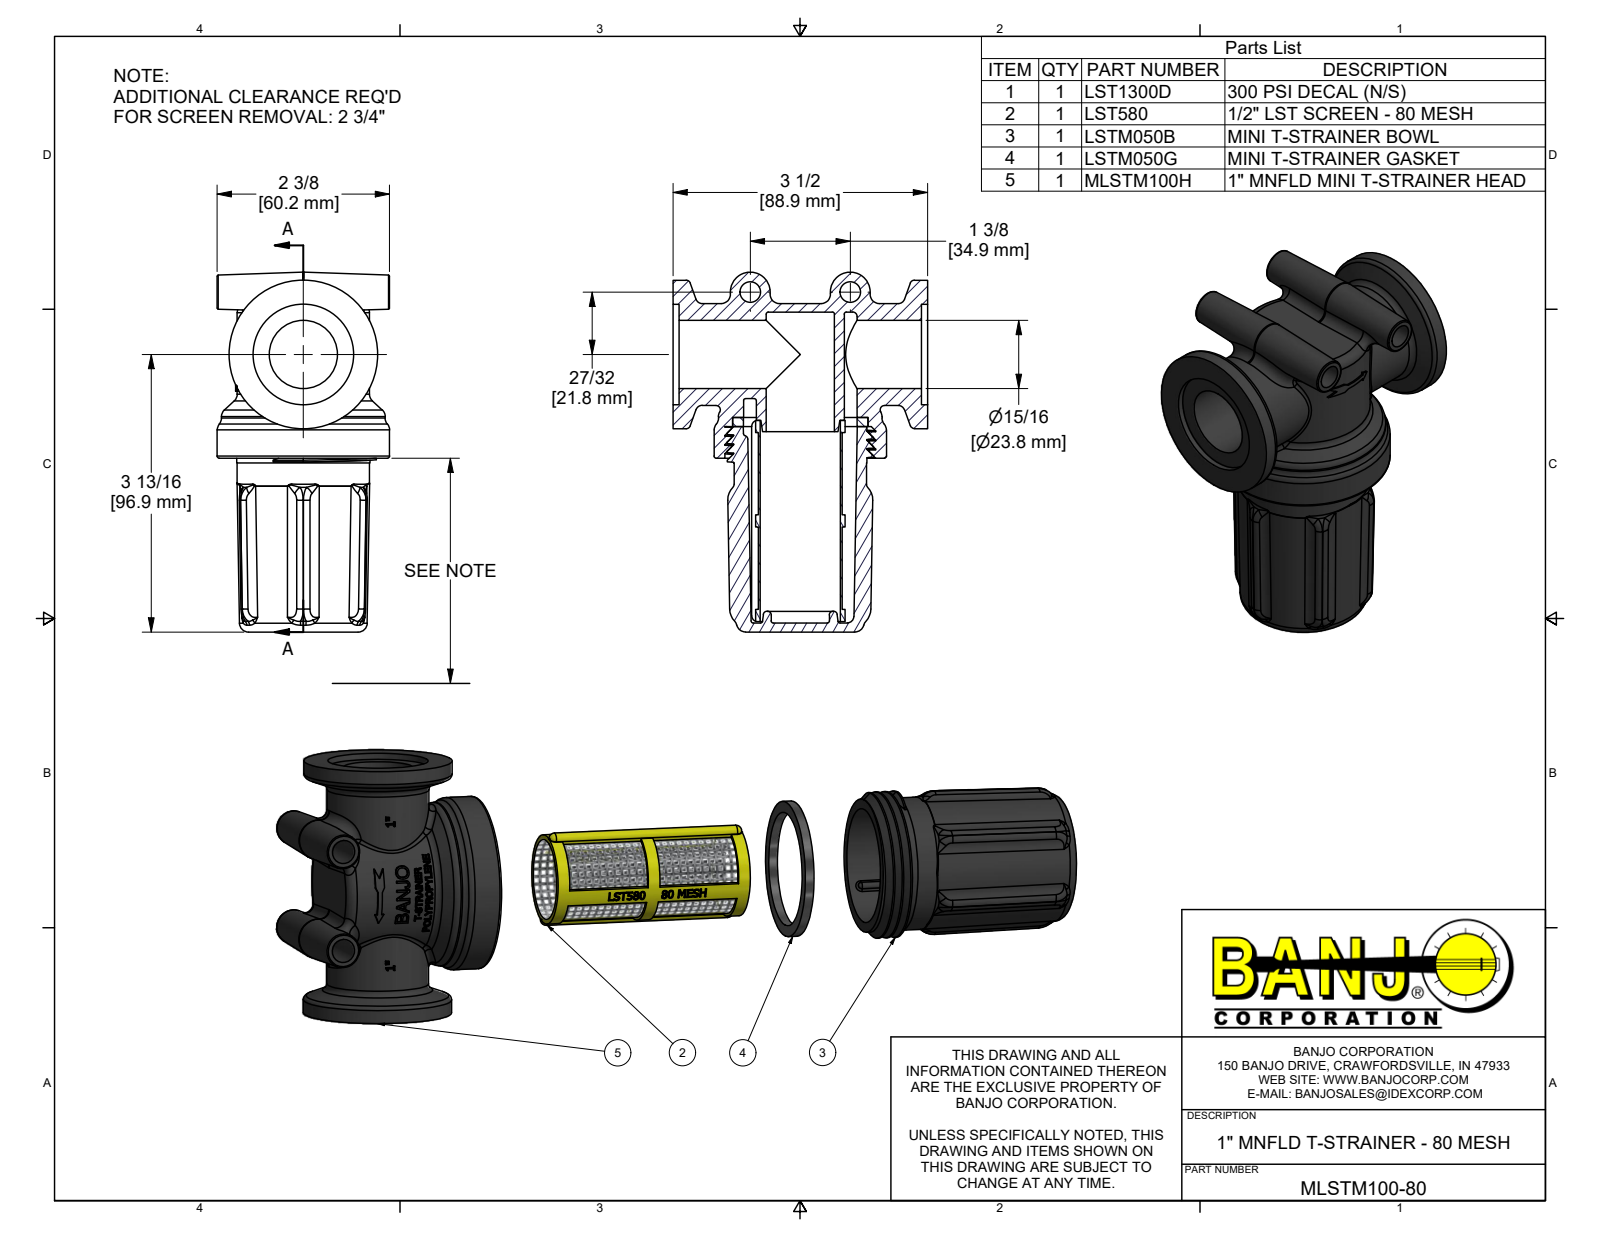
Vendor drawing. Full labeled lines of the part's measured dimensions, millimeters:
Part name (STEP PRODUCT): MLSTM100-80; MLSTM100H; LSTM050G; LSTM050B (+1 more)
STEP written by: Autodesk Inventor 2019 (AUTOMOTIVE_DESIGN)
Units: millimetres
Bodies: 4 solids, 1191 faces (524 planar, 152 cylindrical, 515 other)
Overall size (bounding box): 125.7 × 88.9 × 60.2
Volume: 148 700 mm³ · Surface area: 85 870 mm²
Round holes (diameter × count): ⌀23.8 ×2, ⌀20.3 ×1, ⌀28 ×1, ⌀35.1 ×1, ⌀39.6 ×1, ⌀39.7 ×1, ⌀48 ×1, ⌀52.7 ×1
Round bosses / shafts (diameter × count): ⌀60.2 ×1, ⌀57.2 ×1, ⌀51.8 ×1, ⌀51.1 ×1, ⌀47.3 ×1, ⌀47.2 ×1, ⌀46.6 ×1, ⌀46.2 ×1
Partial cylindrical surfaces — rounded edges, fillets, slot ends (radius × count): R2 ×6, R0.8 ×4, R1.3 ×3, R2.1 ×2, R14 ×1, R14.6 ×1, R15.1 ×1, R15.4 ×1
Main face-to-face distances: 71.8, 88.9, 3.2, 2.1, 86.8, 74.9, 114.7, 42.9, 39.8, 111.7
